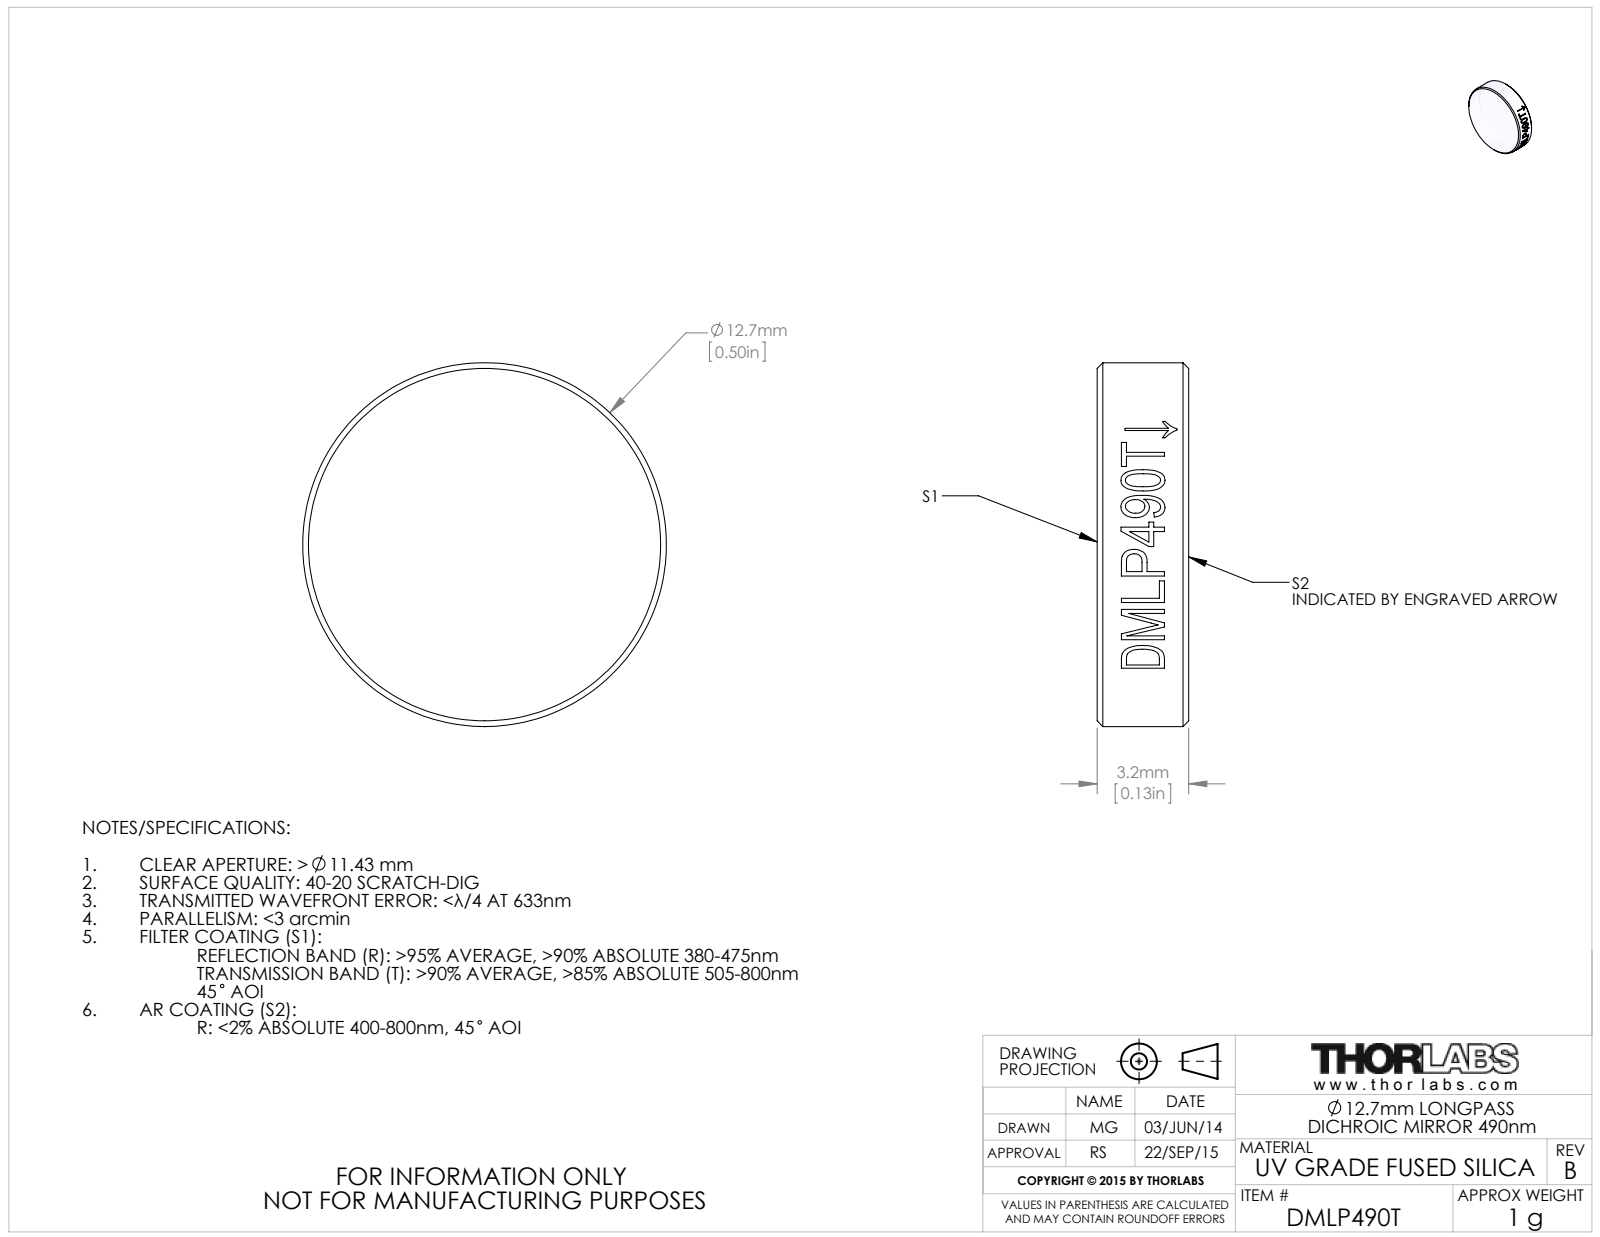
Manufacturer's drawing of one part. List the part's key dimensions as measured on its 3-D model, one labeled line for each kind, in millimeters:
Part name (STEP PRODUCT): TTN028304-E0W
STEP written by: SolidWorks 2012 (CONFIG_CONTROL_DESIGN)
Units: millimetres
Bodies: 1 solid, 22 faces (2 planar, 16 cylindrical, 4 other)
Overall size (bounding box): 12.7 × 12.7 × 3.2
Volume: 404 mm³ · Surface area: 372 mm²
Round bosses / shafts (diameter × count): ⌀12.7 ×1
Main face-to-face distances: 3.2
